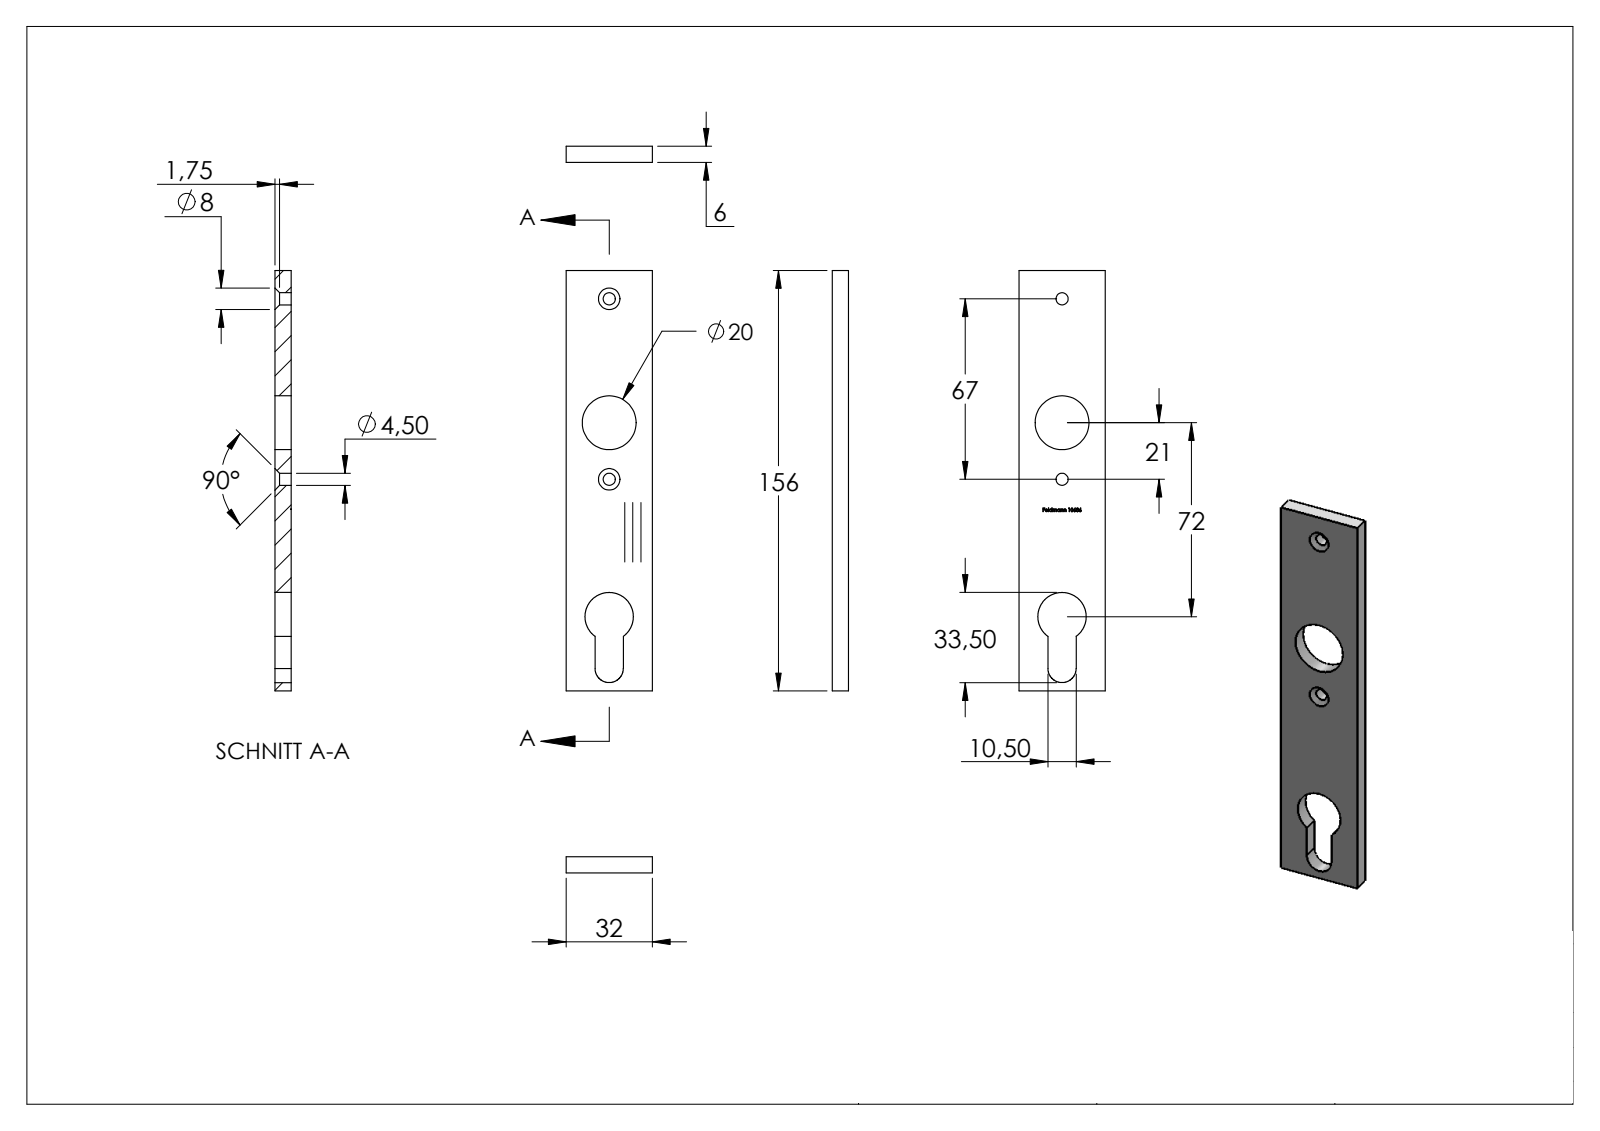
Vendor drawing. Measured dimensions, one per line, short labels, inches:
name: 10686
written by: SolidWorks 2015 (CONFIG_CONTROL_DESIGN)
unit: in
bodies: 1 solid, 201 faces (95 planar, 10 cylindrical, 96 other)
size: 6.142 × 1.26 × 0.236
volume: 1.547 in³; area: 18.25 in²
holes: 2× ⌀0.177, 1× ⌀0.709, 1× ⌀0.787
rounds: 1× R0.207
face distances: 0.236, 1.26, 6.142, 0.423, 0.837, 0.413, 0.232, 0.117, 0.072, 0.015
hole spacings: 0.827, 1.811, 2.008, 2.638, 2.835, 4.646
